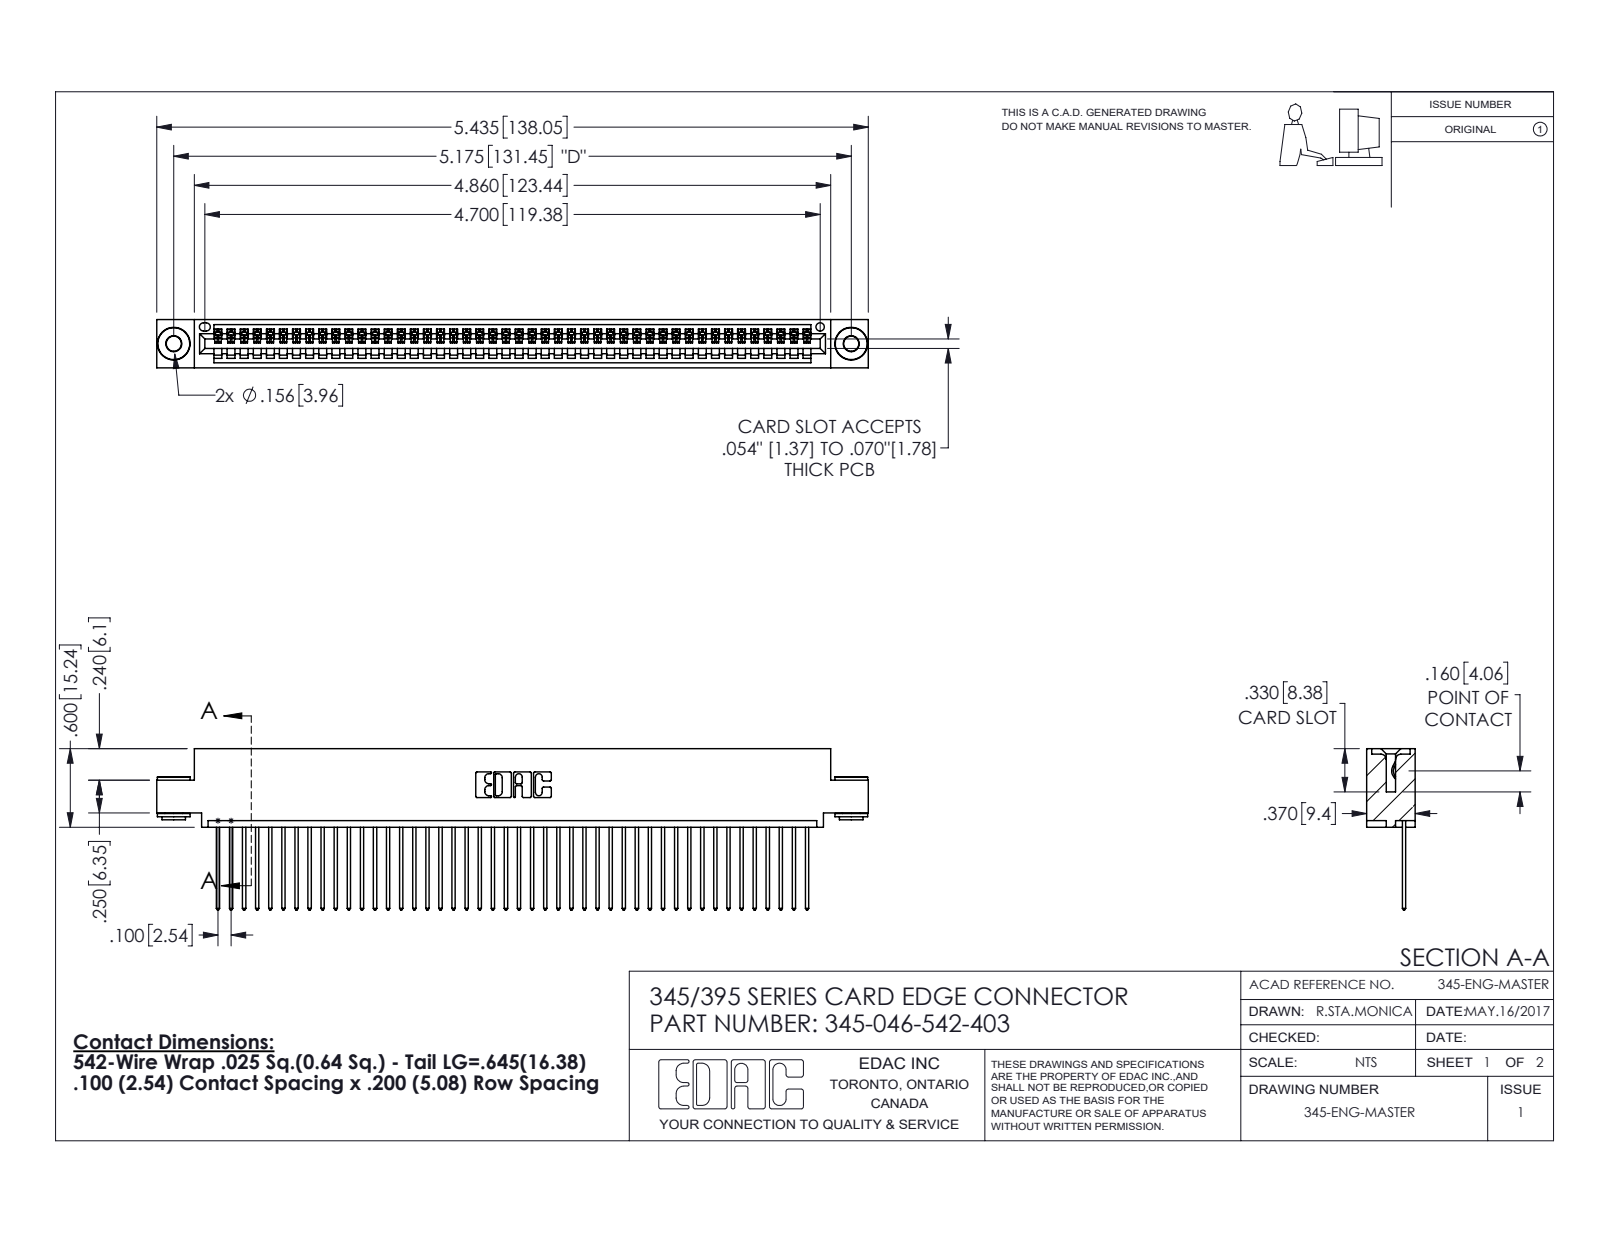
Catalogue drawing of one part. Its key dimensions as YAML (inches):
part_name: "345-292-001_345-293-142; 345 Part_0.110 Offset - 0.156 Dia-TH; 345-046-542-403; 345-250-002_345-250-002-102"
step_written_by: "SolidWorks 2016 (CONFIG_CONTROL_DESIGN)"
units: inches
bodies: {solids: 49, faces: 2836, planar: 1934, cylindrical: 894, other: 8}
overall_size: [5.435, 1.232, 0.37]
volume: 0.805
surface_area: 28.72
round_holes:
  - {diameter: 0.116, count: 2}
  - {diameter: 0.156, count: 2}
  - {diameter: 0.064, count: 1}
round_bosses_or_shafts:
  - {diameter: 0.25, count: 2}
  - {diameter: 0.18, count: 2}
  - {diameter: 0.136, count: 2}
partial_cylinders:
  - {radius: 0.006, count: 92}
  - {radius: 0.01, count: 92}
  - {radius: 0.01, count: 22}
  - {radius: 0.007, count: 6}
  - {radius: 0.031, count: 6}
  - {radius: 0.026, count: 3}
  - {radius: 0.031, count: 2}
  - {radius: 0.04, count: 2}
face_to_face_distances: [0.072, 0.298, 0.025, 0.37, 0.098, 0.272, 0.2, 0.225, 0.149, 0.072]
hole_center_spacings: [0.27, 4.939, 5.175]
